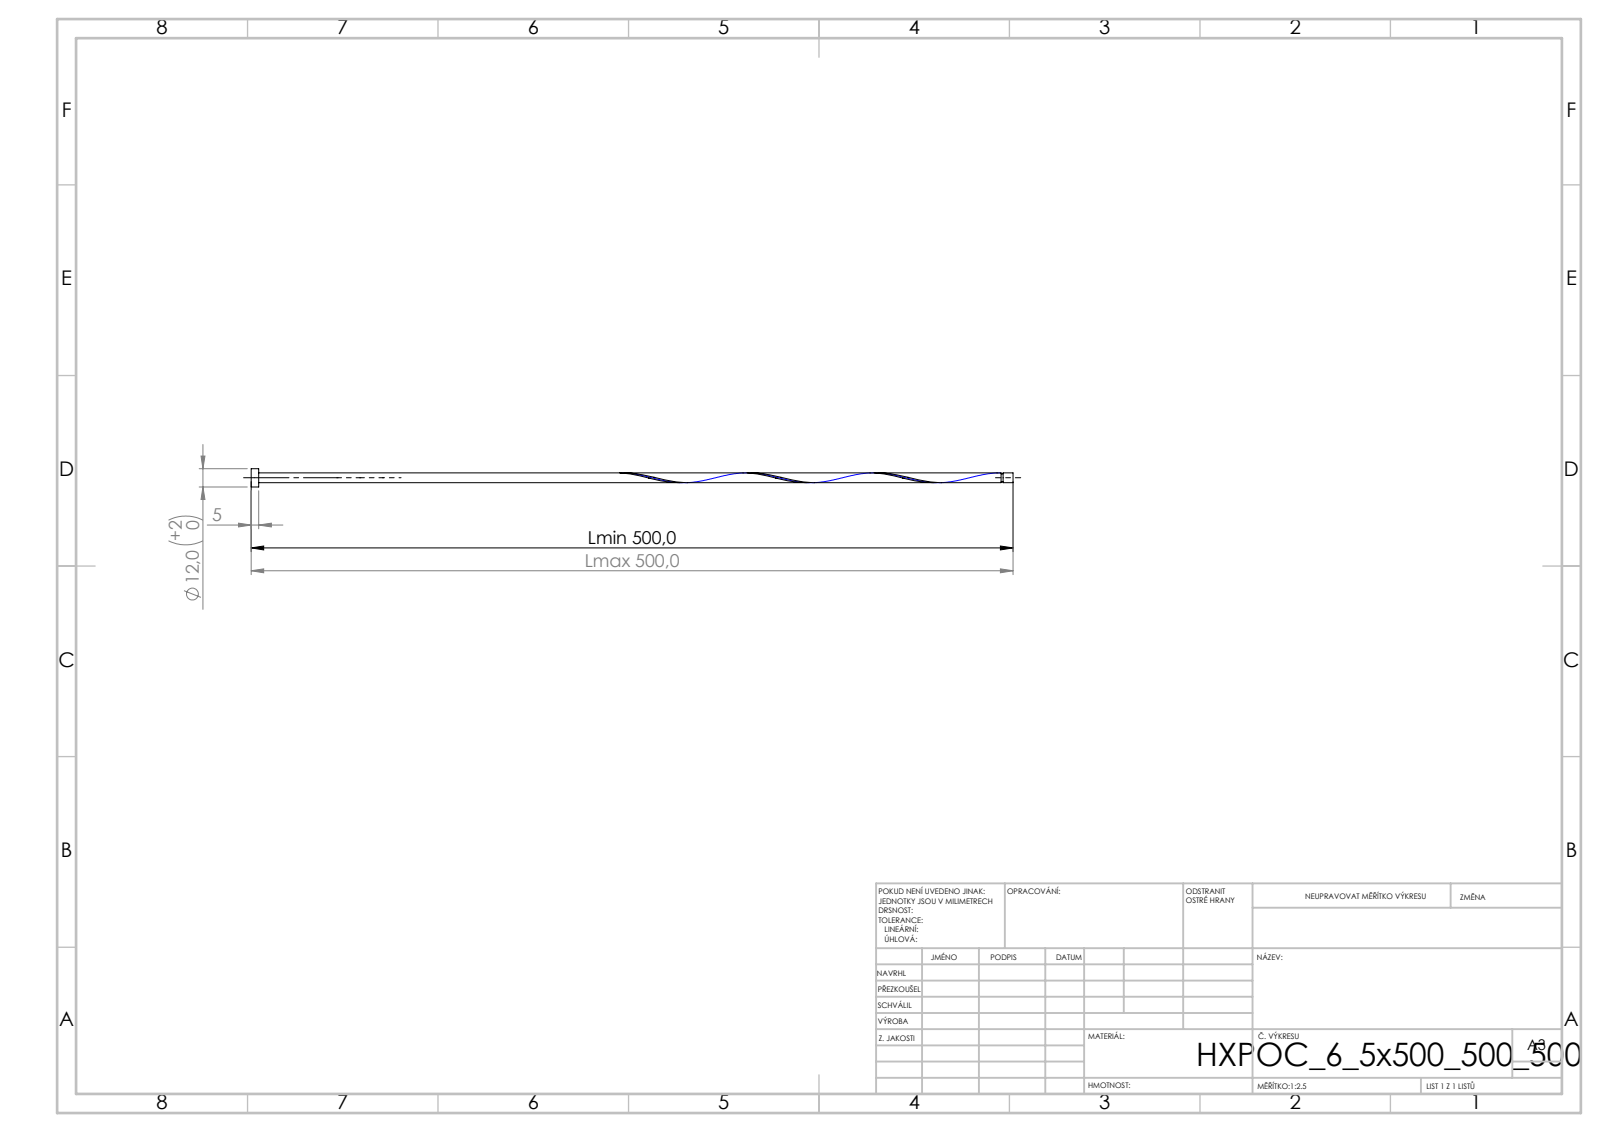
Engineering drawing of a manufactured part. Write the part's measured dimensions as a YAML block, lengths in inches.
step_written_by: "SolidWorks 2019 (CONFIG_CONTROL_DESIGN)"
units: inches
bodies: {solids: 1, faces: 16, planar: 6, cylindrical: 9, other: 1}
overall_size: [19.685, 0.472, 0.472]
volume: 1.251
surface_area: 21.86
round_bosses_or_shafts:
  - {diameter: 0.472, count: 1}
  - {diameter: 0.256, count: 1}
  - {diameter: 0.205, count: 1}
face_to_face_distances: [0.197, 19.685, 19.488, 19.426, 19.23, 0.259, 19.375, 19.178, 0.051, 0.31]
